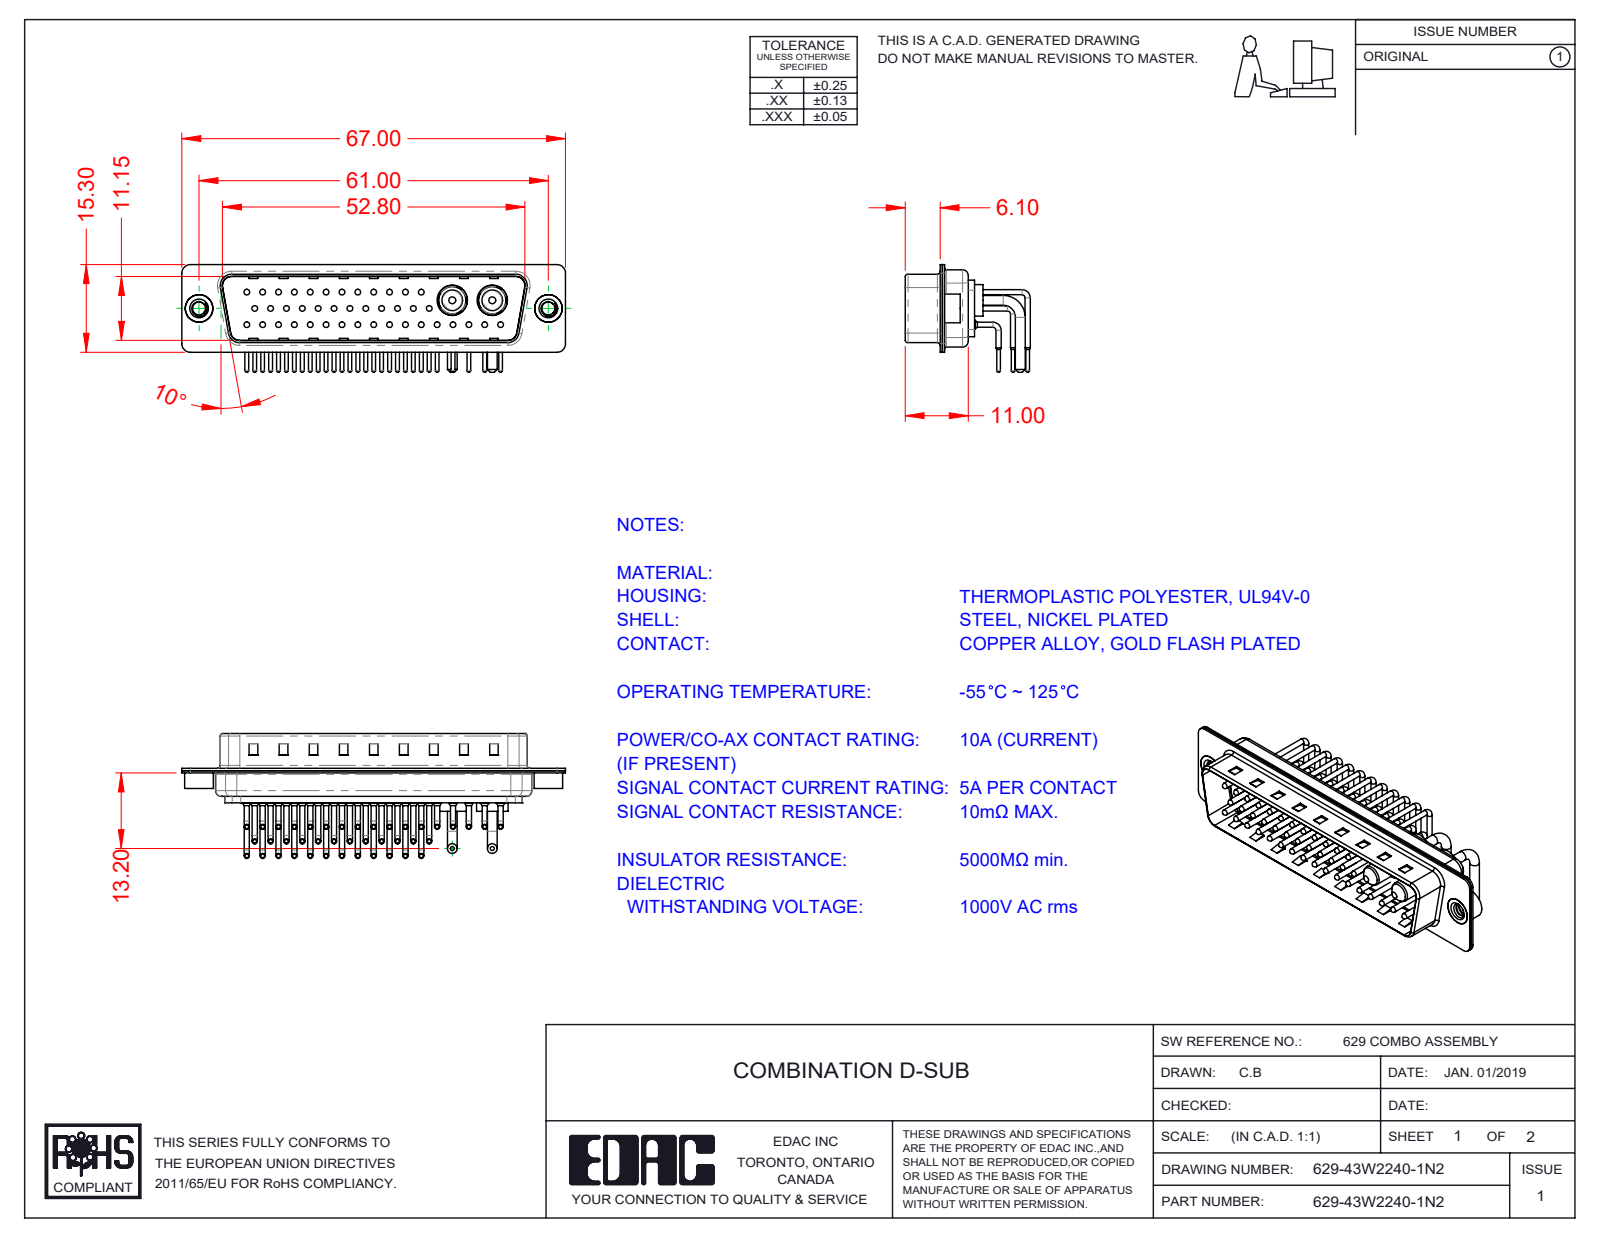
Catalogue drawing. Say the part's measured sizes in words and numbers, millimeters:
The part is named "629Combo Housing_43W2; 629Combo Contact Row 3; 629Combo Shell Front_50 Contacts; 629Combo Threaded Rivet_2 (+5 more)". Its 3-D file was written by "SolidWorks 2020 (CONFIG_CONTROL_DESIGN)". It is 50 solids with 5008 faces: 2847 planar, 1659 cylindrical and 502 other. Overall it measures 67 by 21.83 by 18.8 millimeters. Its volume is 5 088 cubic millimeters and its surface area 12 487 square millimeters. Round holes: 41 of diameter 0.75, 41 of diameter 1.6, 41 of diameter 2, 2 of diameter 2.26, 2 of diameter 4, 2 of diameter 4.8, 2 of diameter 4.85, 2 of diameter 5.3. Round bosses or shafts: 82 of diameter 0.9, 41 of diameter 1.5, 41 of diameter 1, 41 of diameter 0.65, 4 of diameter 1.7, 2 of diameter 5.5, 2 of diameter 5.2, 2 of diameter 5. Partial cylindrical surfaces (rounded edges, fillets, slot ends): 41 of radius 1.01, 16 of radius 1.5, 12 of radius 2, 8 of radius 0.5, 8 of radius 1.6, 4 of radius 0.25, 4 of radius 0.6, 4 of radius 0.65. The main face-to-face distances are 0.4, 11.55, 5.6, 4.1, 6, 1.5, 0.78, 0.77, 12.33, 1.1. The hole center spacings are 2.77, 5.54, 3.16, 8.31, 11.08, 13.85, 16.62, 19.39.
